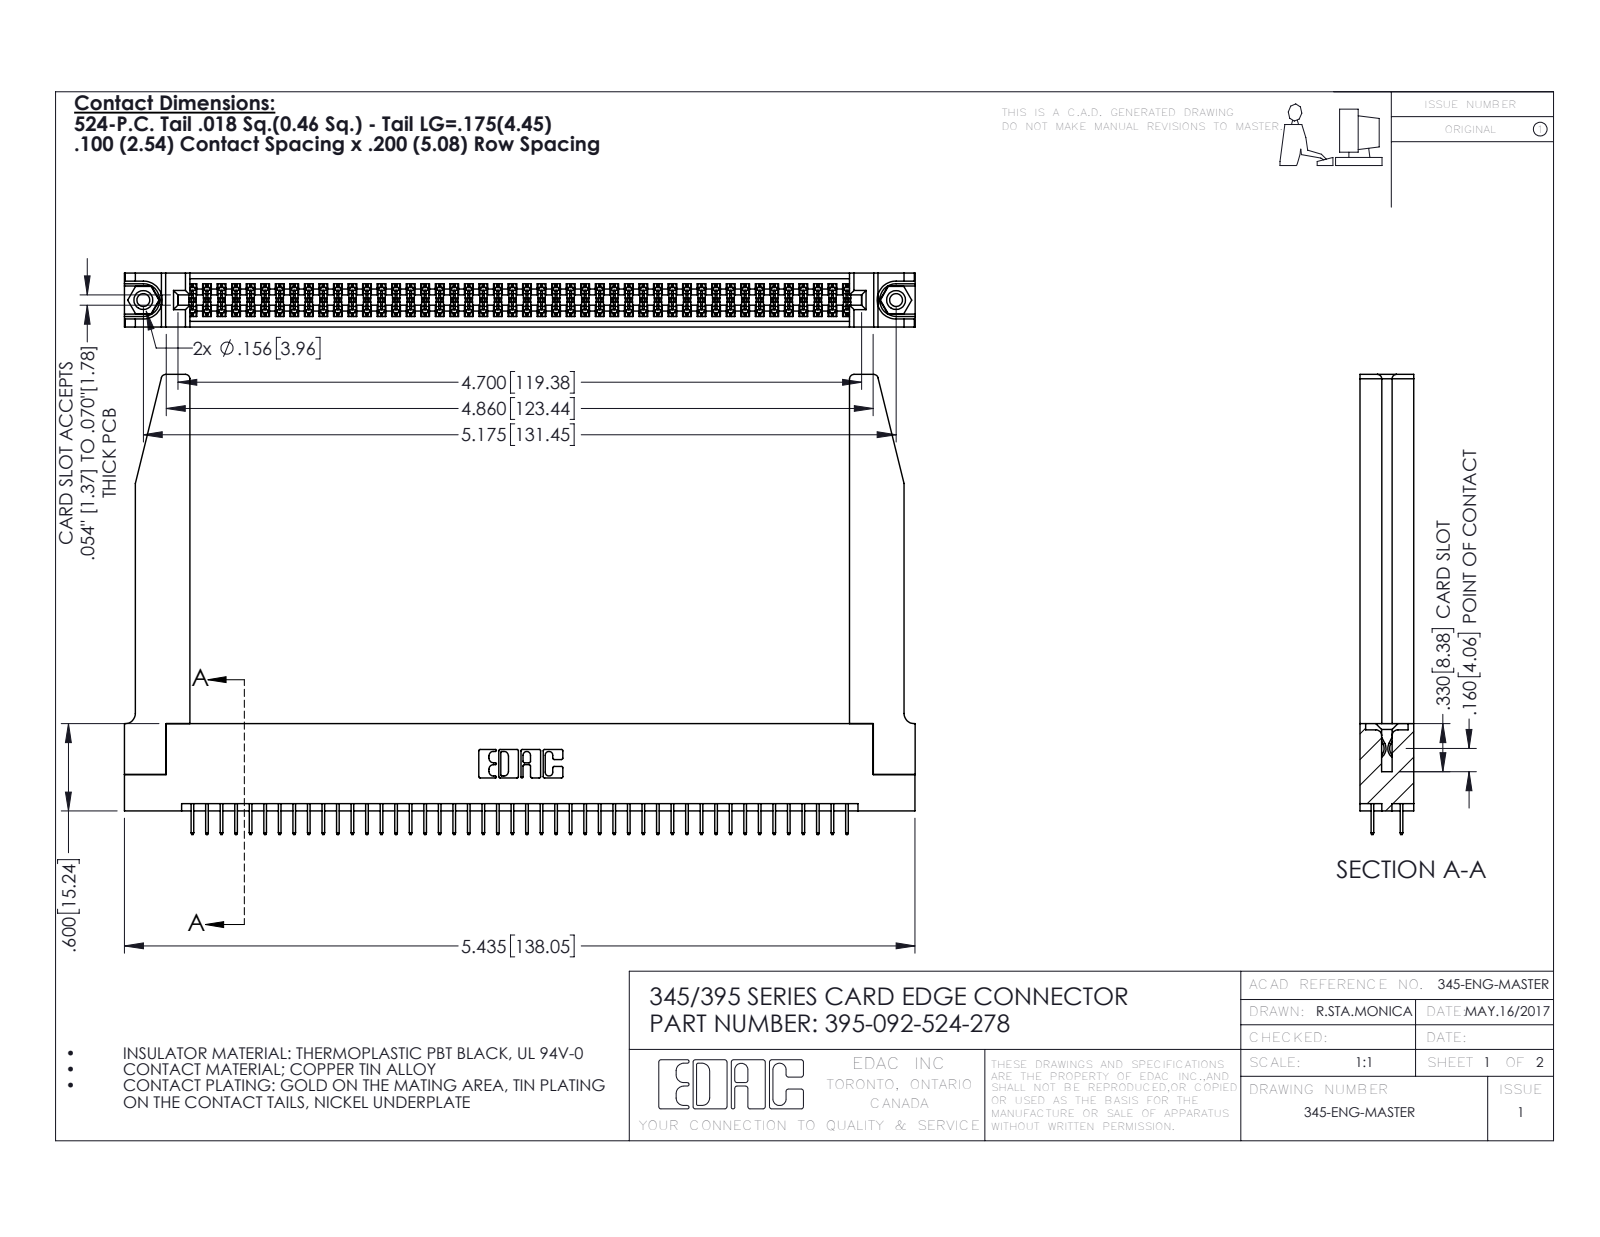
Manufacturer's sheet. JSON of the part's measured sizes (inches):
{"part_name": "345 Part_Flush Mounting Lugs - 0.156 Dia-TH; 345-250-001_345-250-001-102; 345-292-001_345-293-124; 395-092-524-278 (+1 more)", "step_written_by": "SolidWorks 2016 (CONFIG_CONTROL_DESIGN)", "units": "inches", "bodies": {"solids": 97, "faces": 5328, "planar": 3810, "cylindrical": 1466, "other": 52}, "overall_size": [5.436, 3.162, 0.37], "volume_in3": 1.286, "surface_area_in2": 40.65, "round_holes": [[0.089, 2], [0.125, 2], [0.156, 2], [0.064, 1]], "round_bosses_or_shafts": [[0.155, 2]], "partial_cylinders_radius": [[0.006, 138], [0.01, 22], [0.03, 8], [0.007, 6], [0.031, 6], [0.026, 3], [0.014, 2], [0.019, 2]], "face_to_face_distances": [0.37, 0.072, 0.298, 0.2, 0.098, 0.272, 0.025, 0.225, 0.148, 0.15], "hole_center_spacings": [0.27, 4.939, 5.175]}
